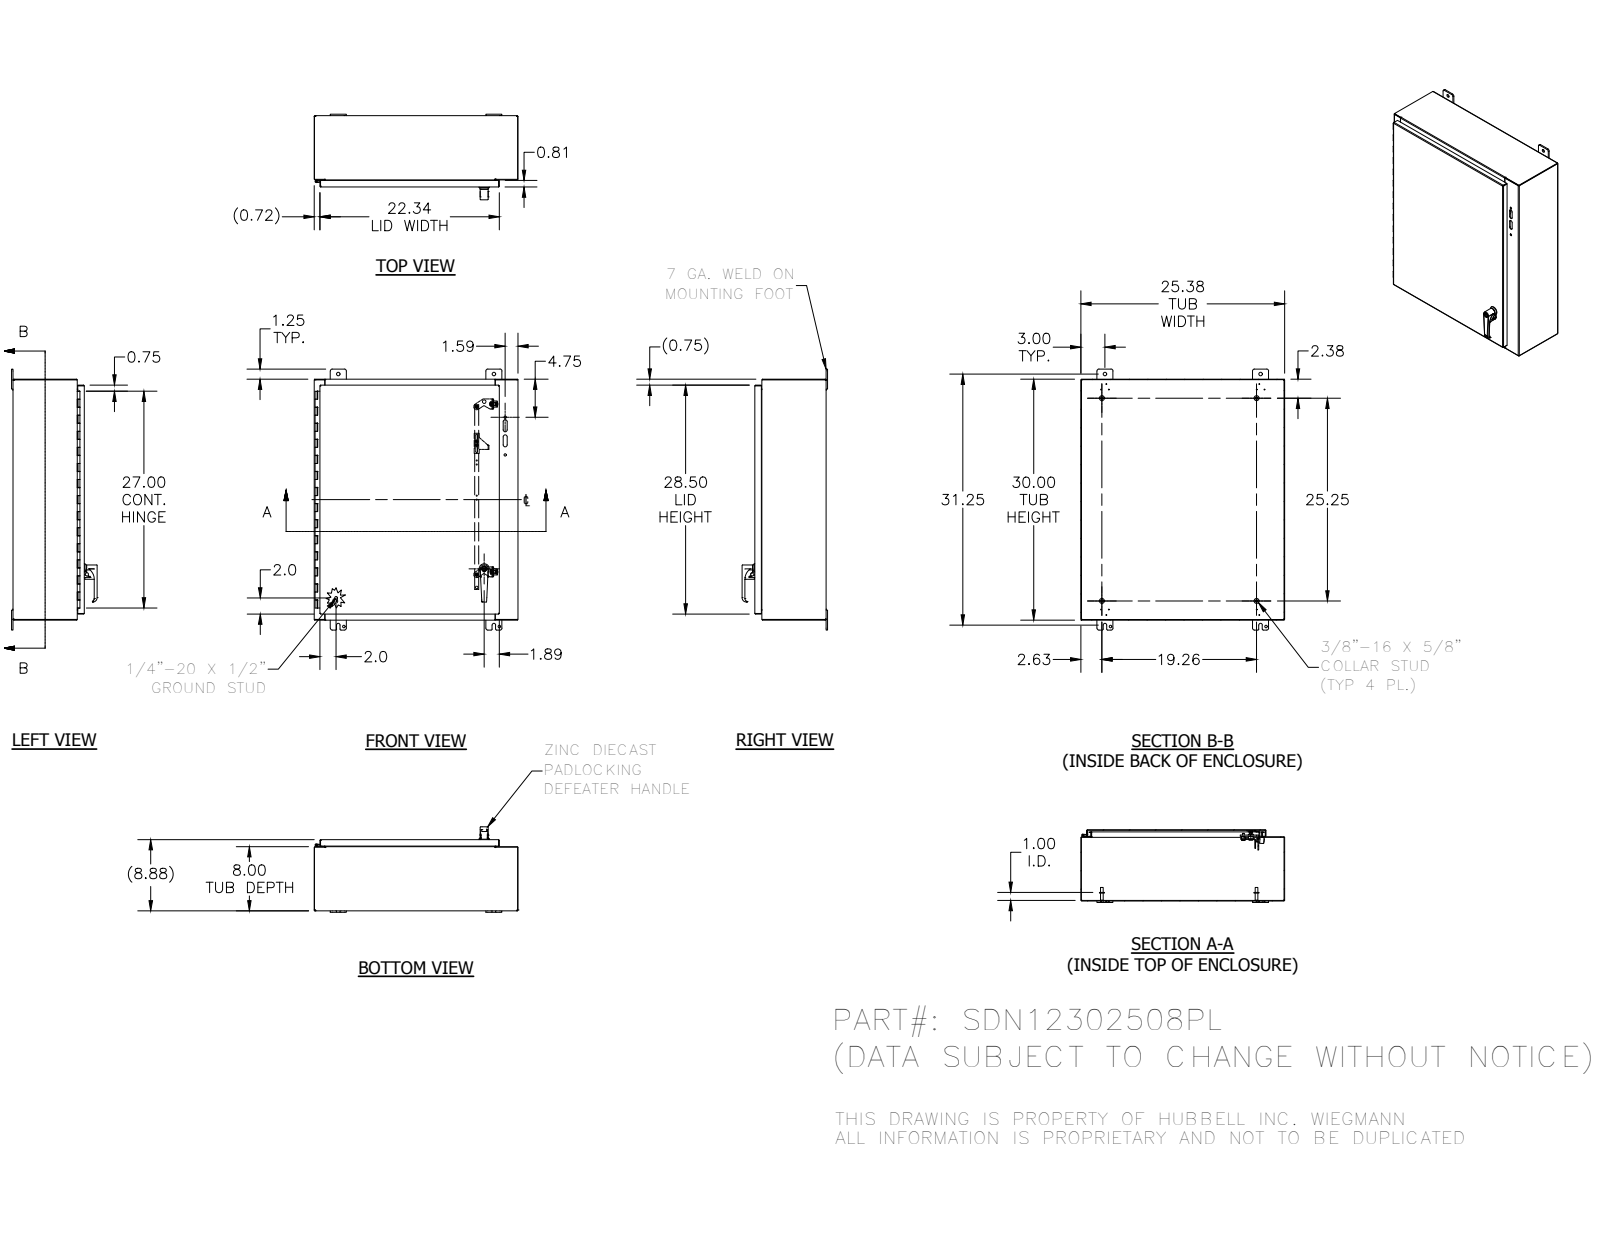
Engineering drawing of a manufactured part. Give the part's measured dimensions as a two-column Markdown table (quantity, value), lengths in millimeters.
| quantity | value |
| --- | --- |
| part name | SDN12302508PL; SDN12302508PLBKP; 388116; 34840 (+8 more) |
| STEP written by | Autodesk Inventor 2012 (AUTOMOTIVE_DESIGN) |
| units | millimeters |
| bodies | 49 solids, 1618 faces (836 planar, 557 cylindrical, 225 other) |
| overall size | 825.5 × 644.7 × 270.5 |
| volume | 3 382 000 mm³ |
| surface area | 3 552 000 mm² |
| round holes (diameter × count) | 3 × 12, 3.7 × 6, 8 × 4, 11.1 × 4, 8.1 × 3, 4 × 2, 5 × 2, 5.4 × 2, 5.6 × 2, 7.1 × 2, 8 × 2, 11.4 × 2 |
| round bosses / shafts (diameter × count) | 15.9 × 5, 8.4 × 5, 11.1 × 4, 7.6 × 4, 6.4 × 4, 5.7 × 4, 4.8 × 4, 19.1 × 2 |
| partial cylindrical surfaces (radius × count) | 0.5 × 38, 0.3 × 31, 6.4 × 22, 0.8 × 20, 2.7 × 20, 3.2 × 17, 0.6 × 16, 1.8 × 8 |
| main face-to-face distances | 1.9, 223.5, 221.7, 225.4, 642.8, 760.1, 201.3, 22.2, 640.9, 644.7 |
| hole center spacings | 530.9, 19.3, 40.5, 476.2, 492.3, 695.5, 712.9, 713 |
